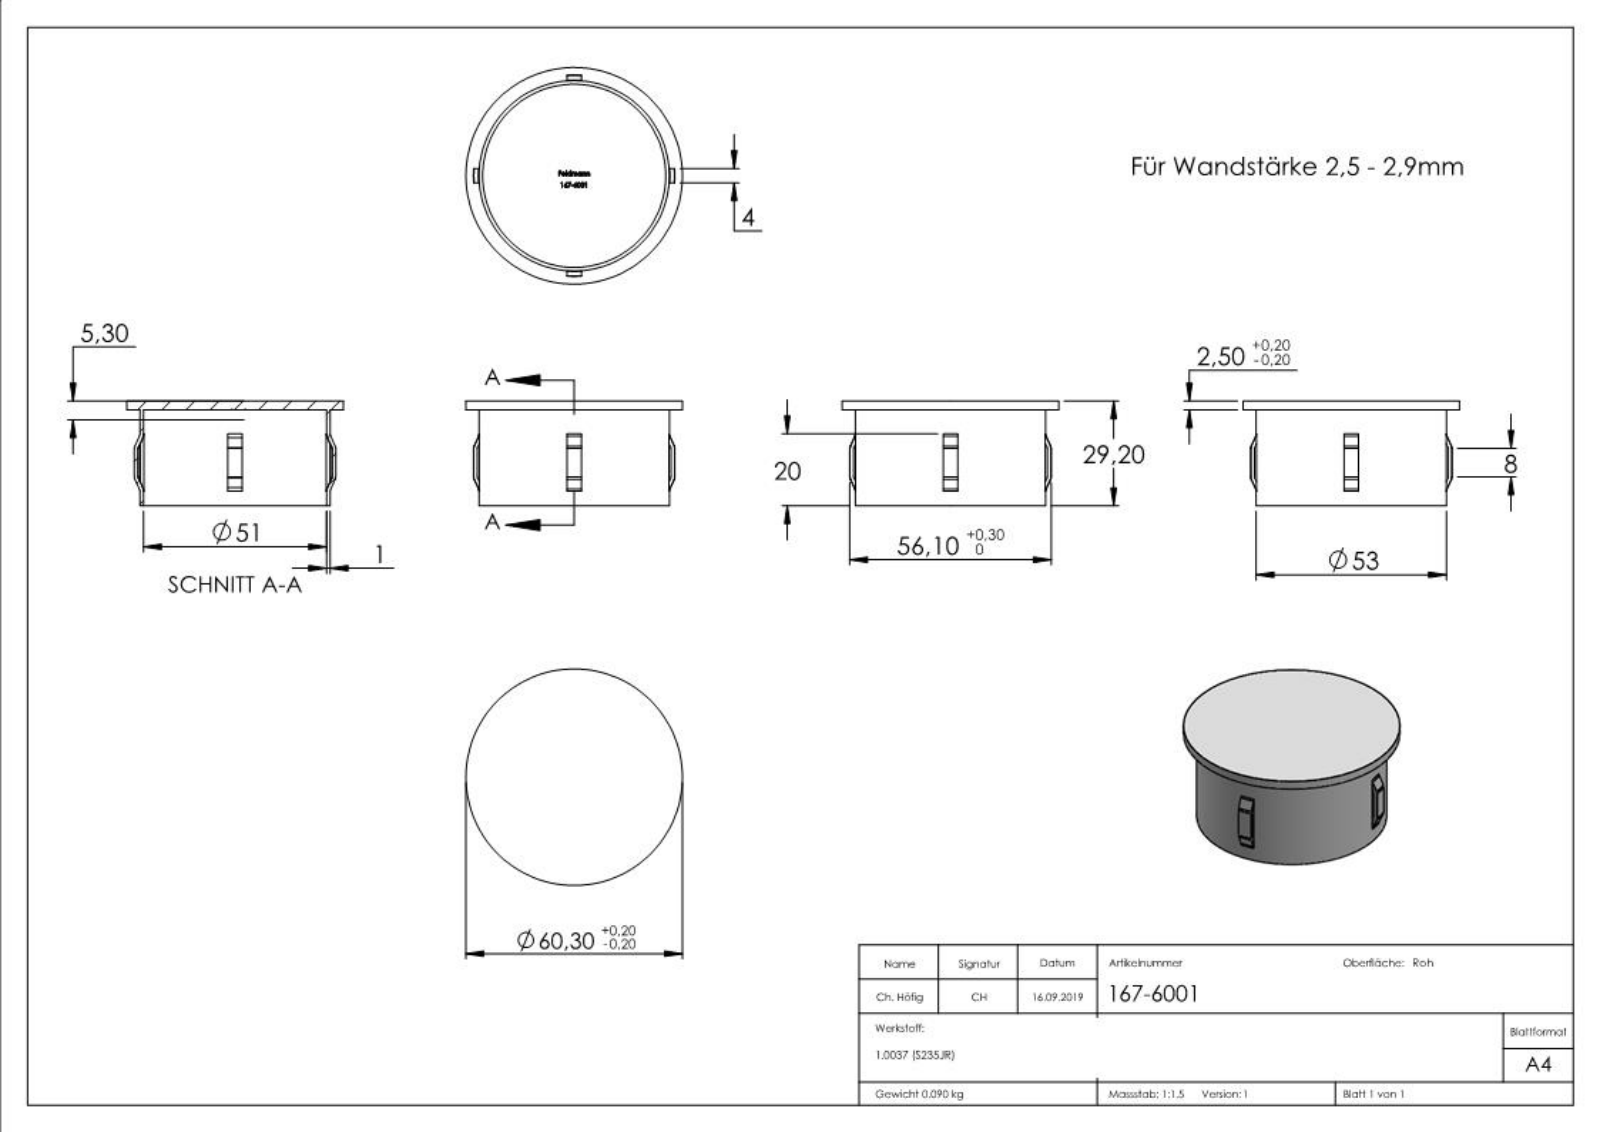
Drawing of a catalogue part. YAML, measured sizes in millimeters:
part_name: "167-6001"
step_written_by: "SolidWorks 2015 (CONFIG_CONTROL_DESIGN)"
units: millimeters
bodies: {solids: 1, faces: 285, planar: 125, cylindrical: 16, other: 144}
overall_size: [60.3, 60.3, 29.2]
volume: 11511
surface_area: 15148
round_holes:
  - {diameter: 51, count: 1}
round_bosses_or_shafts:
  - {diameter: 60.3, count: 1}
  - {diameter: 53, count: 1}
partial_cylinders:
  - {radius: 27.05, count: 1}
  - {radius: 28.05, count: 1}
face_to_face_distances: [2.5, 26.7, 29.2, 4, 2.4, 26.8, 2.97, 2, 0.39, 1.26]
